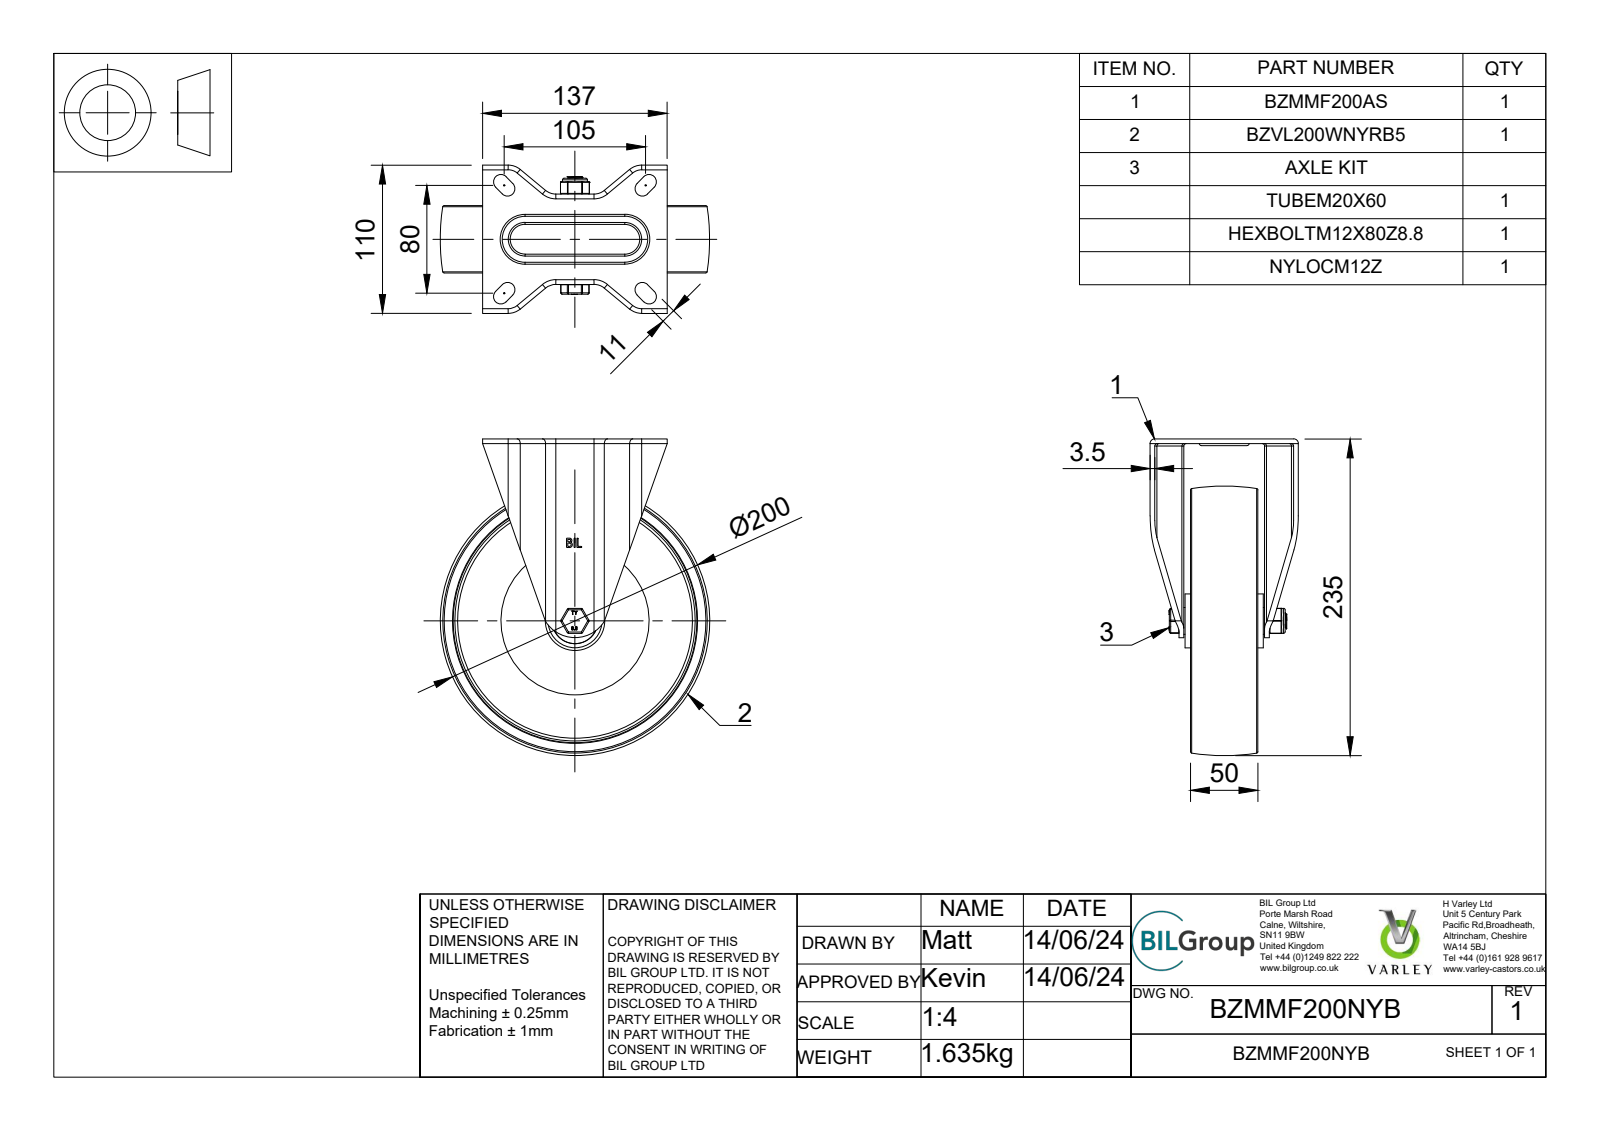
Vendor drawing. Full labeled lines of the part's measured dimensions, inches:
Part name (STEP PRODUCT): BZMMF200NYB v3; BZMMF200AS v1; BZMMF200AS; ZINC PLATED, PRESSED STEEL BRACKET (+8 more)
STEP written by: Autodesk Translation Framework v13.14.0.145 (AUTOMOTIVE_DESIGN)
Units: inches
Bodies: 16 solids, 470 faces (197 planar, 167 cylindrical, 106 other)
Overall size (bounding box): 9.252 × 7.874 × 4.331
Volume: 45.3 in³ · Surface area: 371.1 in²
Round holes (diameter × count): ⌀0.472 ×1, ⌀0.48 ×1, ⌀0.492 ×1, ⌀0.551 ×1, ⌀0.787 ×1, ⌀0.795 ×1
Round bosses / shafts (diameter × count): ⌀0.295 ×8, ⌀1.575 ×1, ⌀1.339 ×1, ⌀0.783 ×1, ⌀0.728 ×1, ⌀0.709 ×1, ⌀0.466 ×1, ⌀0.387 ×1
Partial cylindrical surfaces — rounded edges, fillets, slot ends (radius × count): R0.02 ×18, R0.039 ×12, R0.059 ×8, R0.069 ×8, R0.138 ×8, R0.217 ×8, R0.236 ×4, R0.276 ×4
Main face-to-face distances: 0.138, 0.374, 0.969, 0.994, 1.368, 2.165, 0.197, 1.132, 1.506, 2.5
